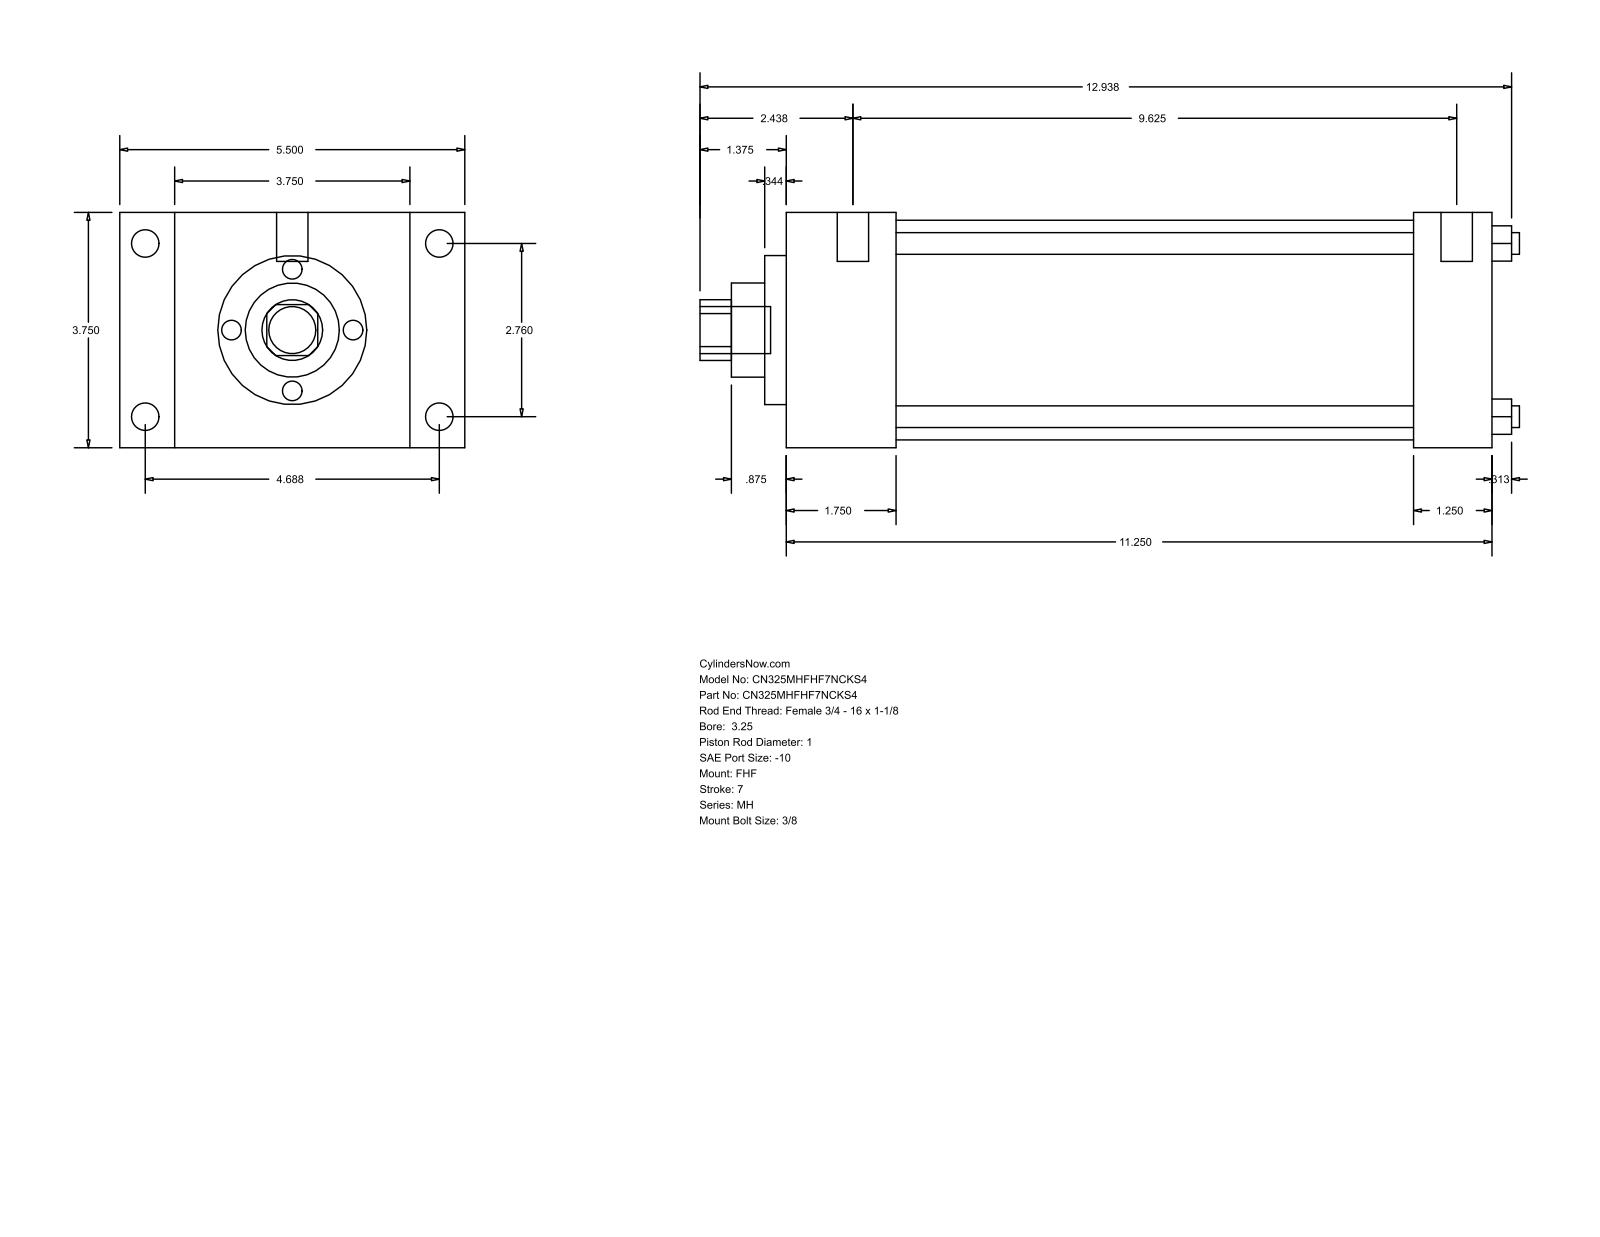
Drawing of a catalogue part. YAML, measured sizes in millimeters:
part_name: "MH_FHF__0325_1"
step_written_by: "GSSL Pune (CONFIG_CONTROL_DESIGN)"
units: millimeters
bodies: {solids: 0, faces: 90, planar: 61, cylindrical: 29, other: 0}
overall_size: [331.79, 139.7, 95.25]
round_holes:
  - {diameter: 8.76, count: 4}
  - {diameter: 25.4, count: 1}
  - {diameter: 38.1, count: 1}
  - {diameter: 60.33, count: 1}
  - {diameter: 88.9, count: 1}
round_bosses_or_shafts:
  - {diameter: 11.13, count: 4}
  - {diameter: 5.56, count: 4}
  - {diameter: 12.7, count: 2}
  - {diameter: 19.05, count: 1}
partial_cylinders:
  - {radius: 12.29, count: 1}
face_to_face_distances: [95.24, 285.76, 44.46, 241.3, 22.23, 117.47, 139.7, 254.01, 209.55, 31.75]
hole_center_spacings: [49.57, 70.1, 99.14]
